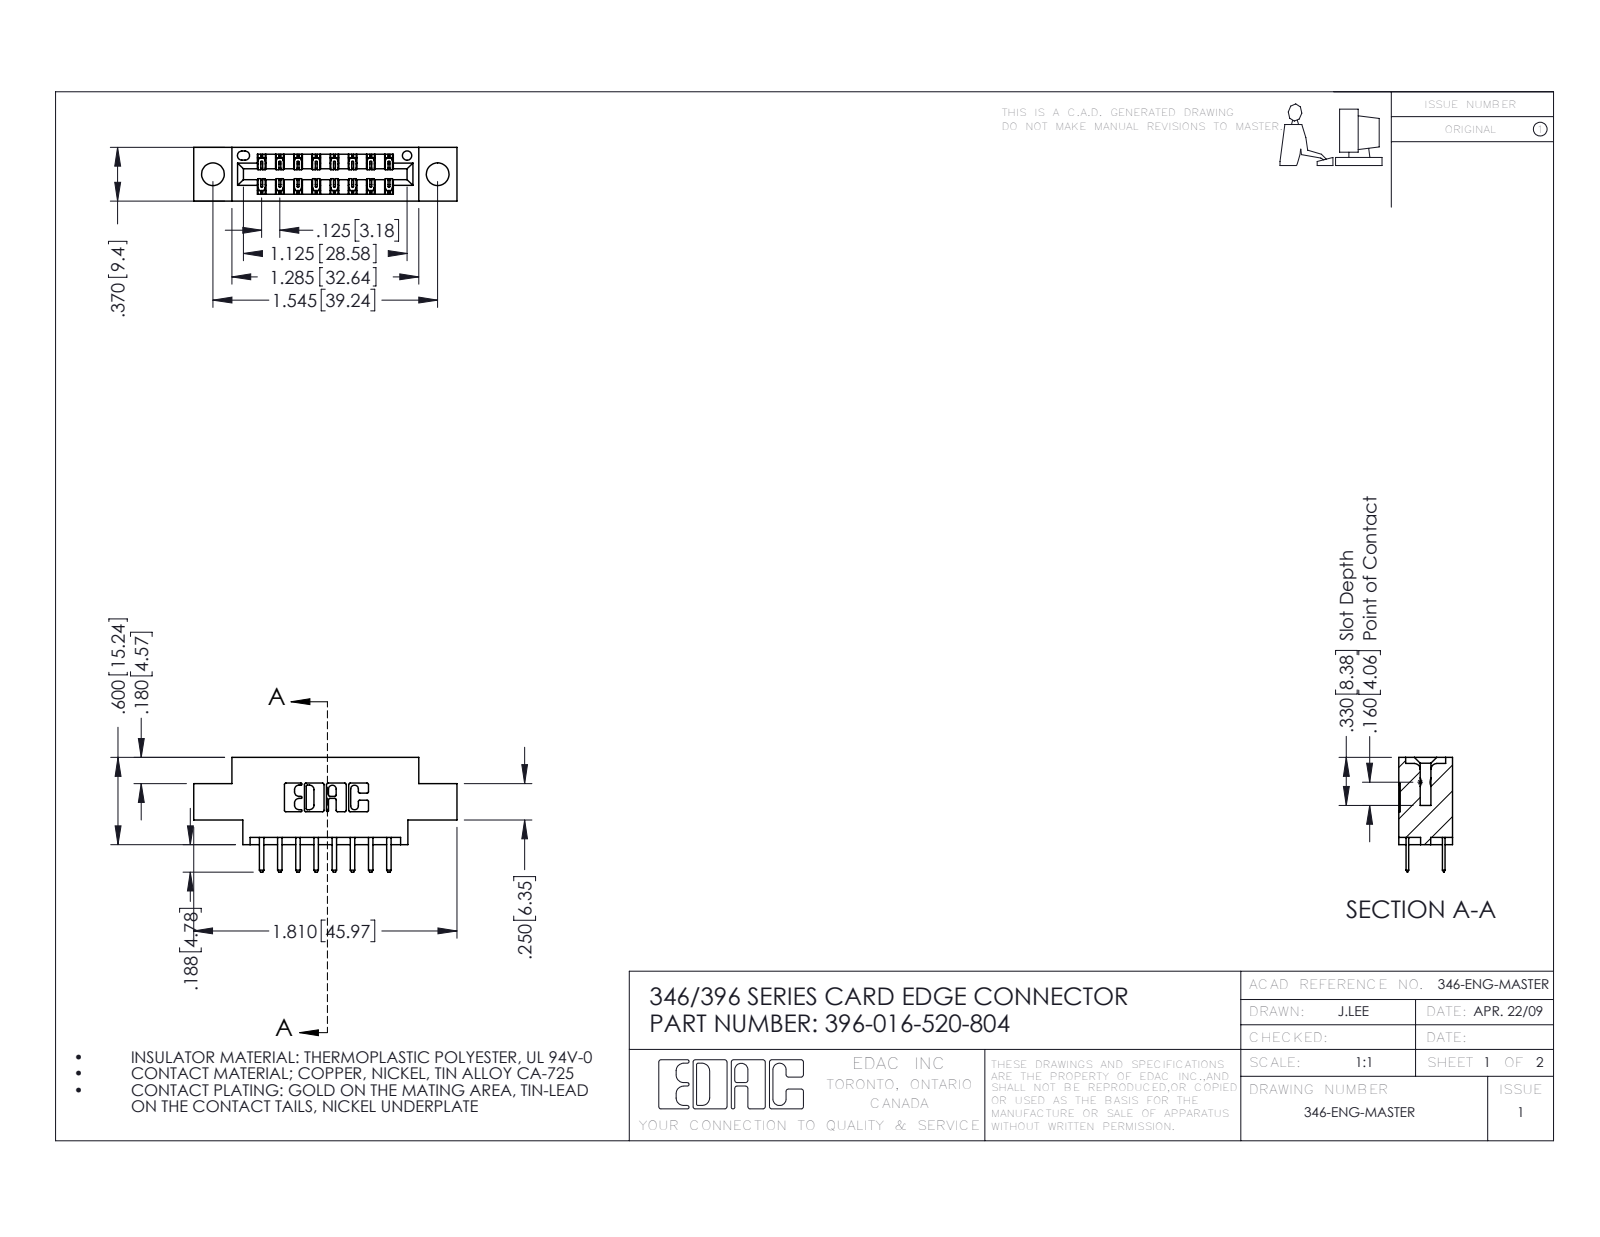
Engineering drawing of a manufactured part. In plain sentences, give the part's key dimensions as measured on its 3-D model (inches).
The part is named "345-292-001_345-293-120; 396-016-520-804; 346 Part_0.170 Offset - 0.156 Dia-TH". Its 3-D file was written by "SolidWorks 2016 (CONFIG_CONTROL_DESIGN)". It is 17 solids with 1022 faces: 672 planar, 350 cylindrical and 0 other. Overall it measures 1.81 by 0.788 by 0.37 inches. Its volume is 0.242 cubic inches and its surface area 7.593 square inches. Round holes: 2 of diameter 0.156, 1 of diameter 0.064. Partial cylindrical surfaces (rounded edges, fillets, slot ends): 24 of radius 0.006, 22 of radius 0.01, 20 of radius 0.01, 6 of radius 0.007, 6 of radius 0.031, 3 of radius 0.026, 2 of radius 0.014, 2 of radius 0.022. The main face-to-face distances are 0.25, 0.37, 0.048, 0.322, 0.148, 0.222, 0.1, 0.174, 0.275, 0.072. The hole center spacings are 0.246, 1.341, 1.545.
